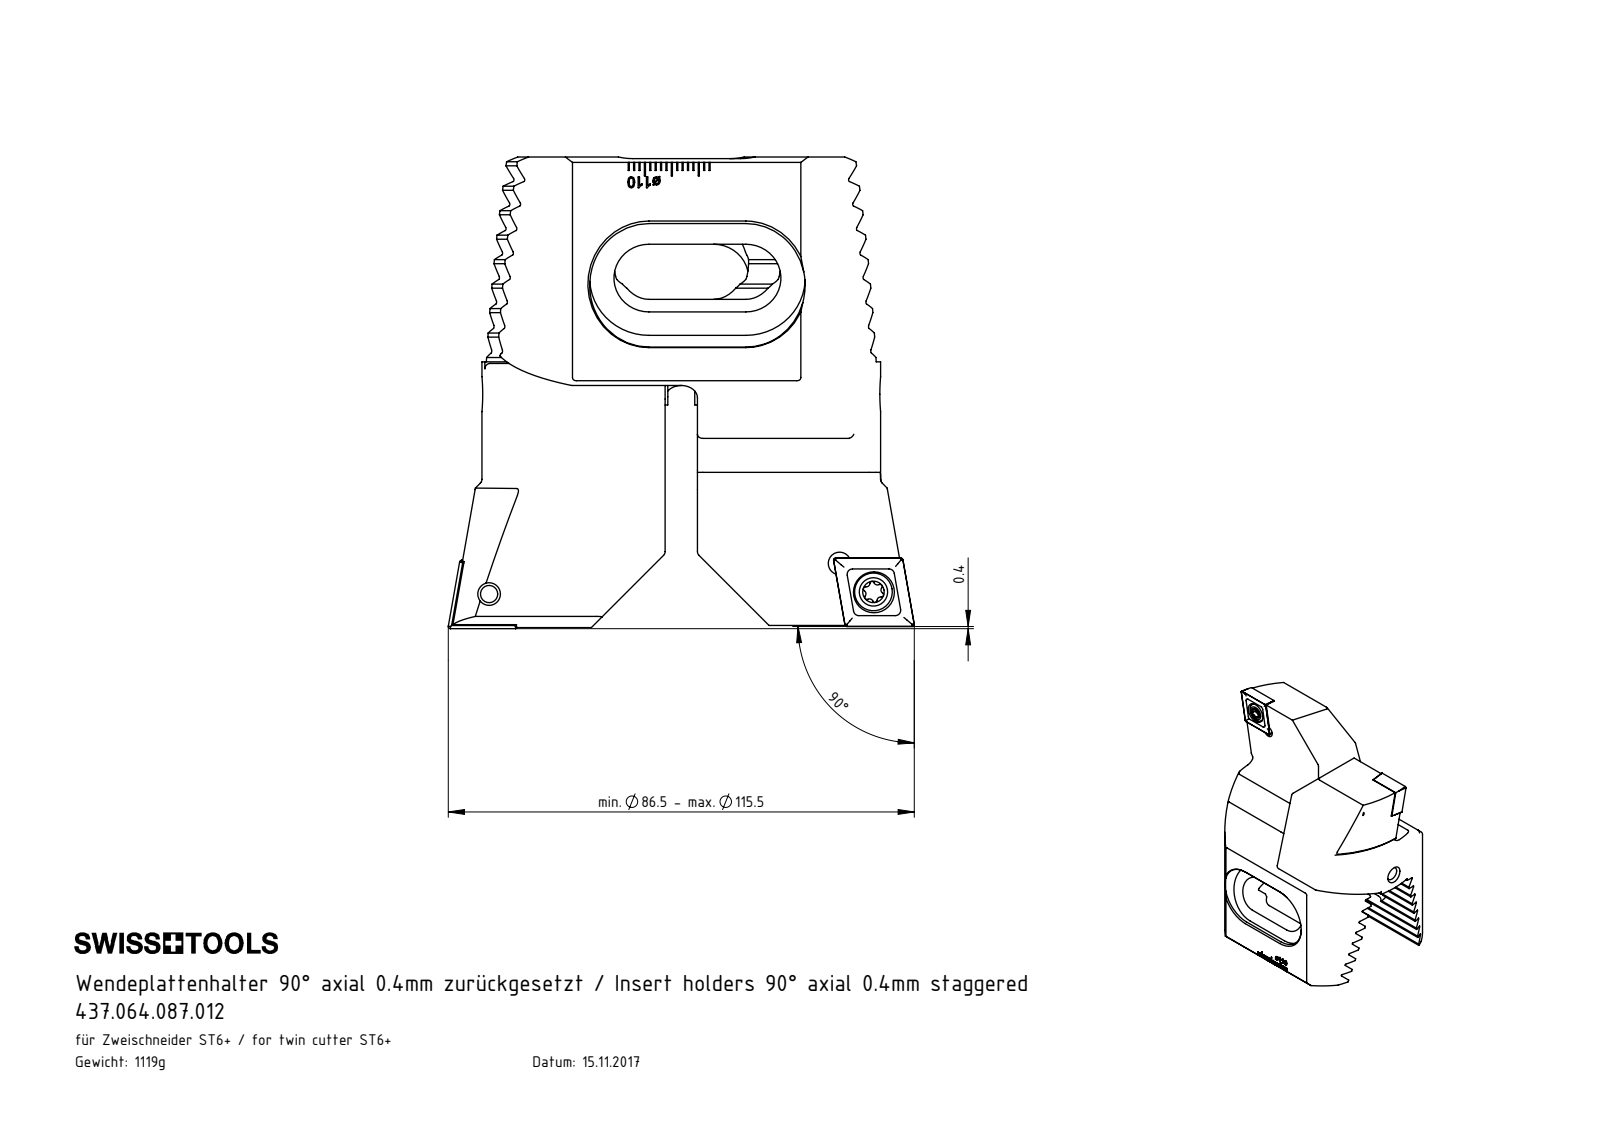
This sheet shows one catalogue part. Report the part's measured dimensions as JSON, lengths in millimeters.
{"part_name": "ZC7-xxx.001.050_A_versetzt Combi; ZC7-xxx.001.050_A; Z72-ER3.001.030; WCC-ER2.001.010_A (+3 more)", "step_written_by": "SolidWorks 2017 (CONFIG_CONTROL_DESIGN)", "units": "millimeters", "bodies": {"solids": 8, "faces": 746, "planar": 411, "cylindrical": 143, "other": 192}, "overall_size": [87.5, 86.5, 58.2], "volume_mm3": 142276, "surface_area_mm2": 37228, "round_holes": [[4.2, 4], [5, 2], [5.5, 2], [7.6, 2], [2, 1], [2.5, 1], [8, 1]], "round_bosses_or_shafts": [[7, 2], [5, 2], [6, 1], [4, 1], [3, 1], [2, 1]], "partial_cylinders_radius": [[0.34, 16], [1, 16], [0.39, 12], [0.69, 6], [0.69, 6], [3, 4], [6.5, 4], [11, 4]], "face_to_face_distances": [4.07, 8.14, 20.36, 12.21, 28.8, 29.4, 58.2, 16.29, 20.34, 24.43], "hole_center_spacings": [8.21, 8.33, 71.43, 20, 58.76, 65.23, 65.3, 65.33]}
